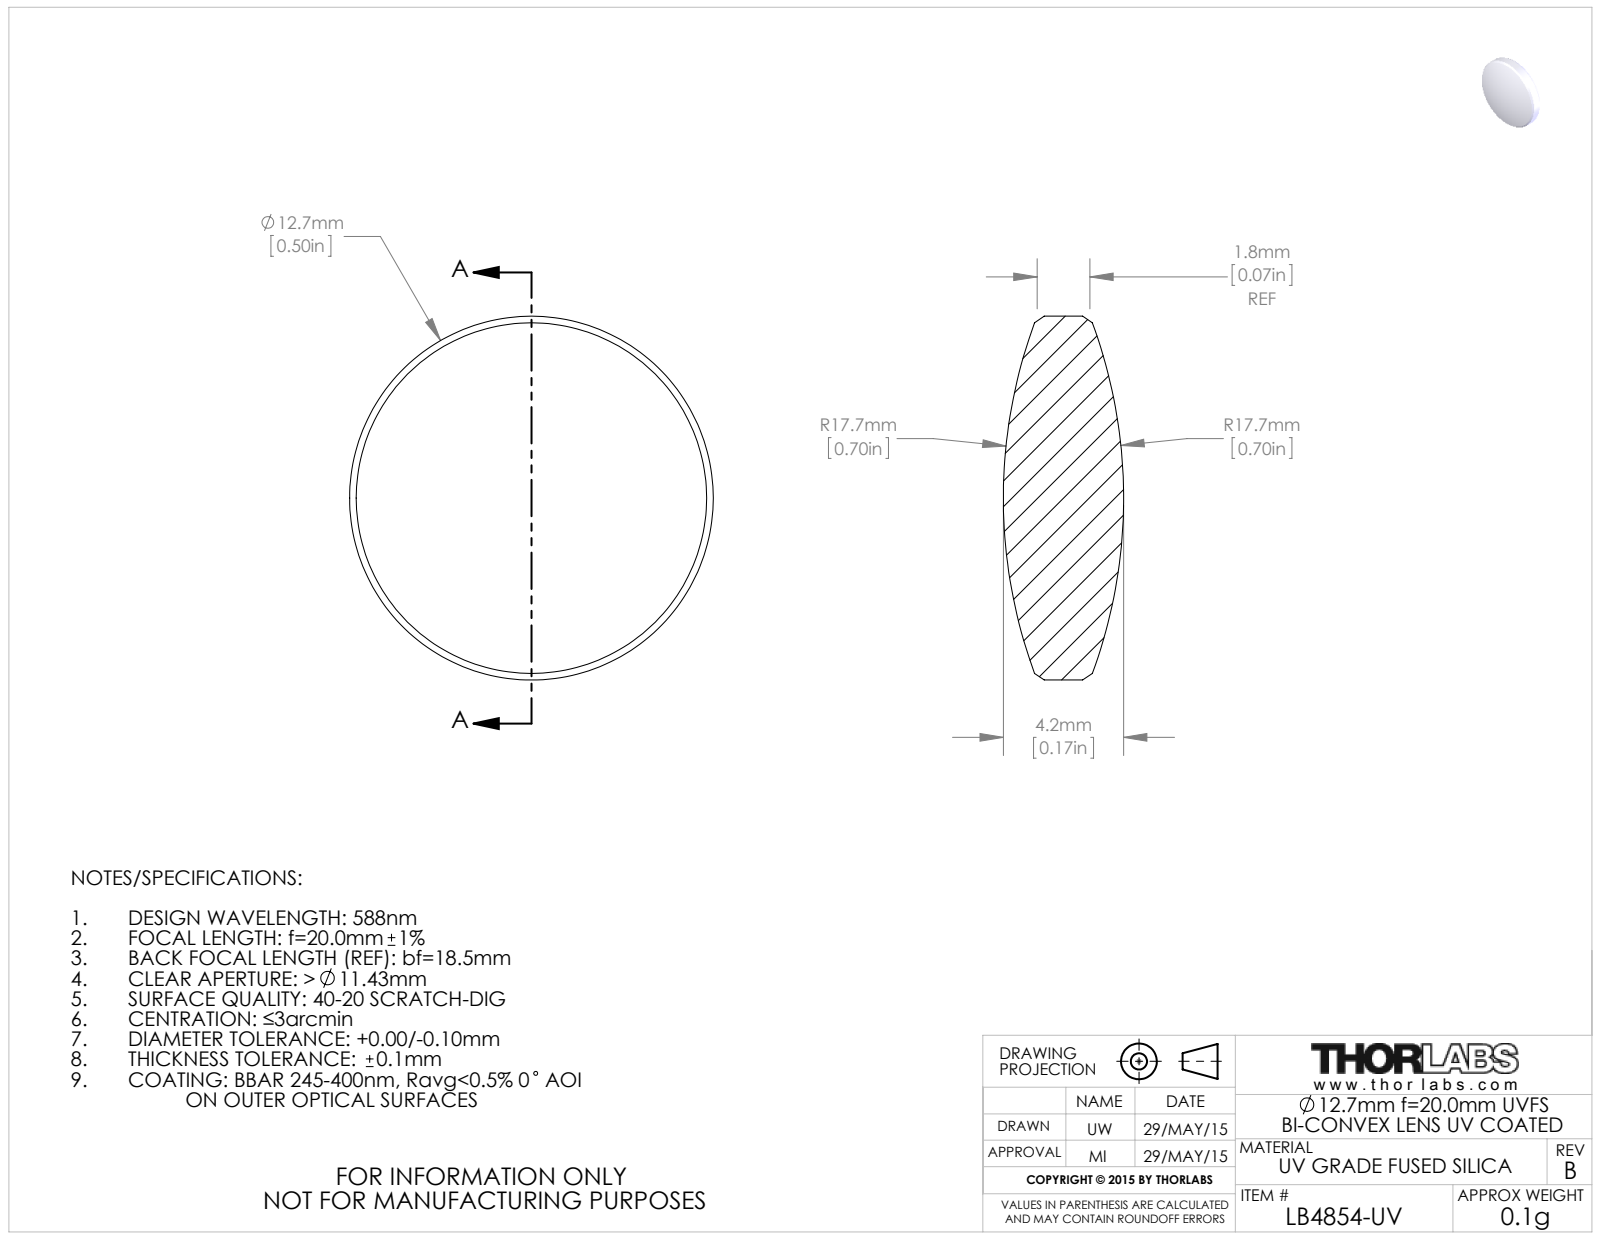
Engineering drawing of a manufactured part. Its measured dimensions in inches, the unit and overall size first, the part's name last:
Units: inches
Overall size (bounding box): 0.5 × 0.5 × 0.165
Round bosses / shafts (diameter × count): ⌀0.5 ×1
Volume: 0.023 in³ · Surface area: 0.508 in²
Bodies: 1 solid, 10 faces (0 planar, 2 cylindrical, 8 other)
Part name (STEP PRODUCT): 4311-E0W
STEP written by: SolidWorks 2014 (CONFIG_CONTROL_DESIGN)
